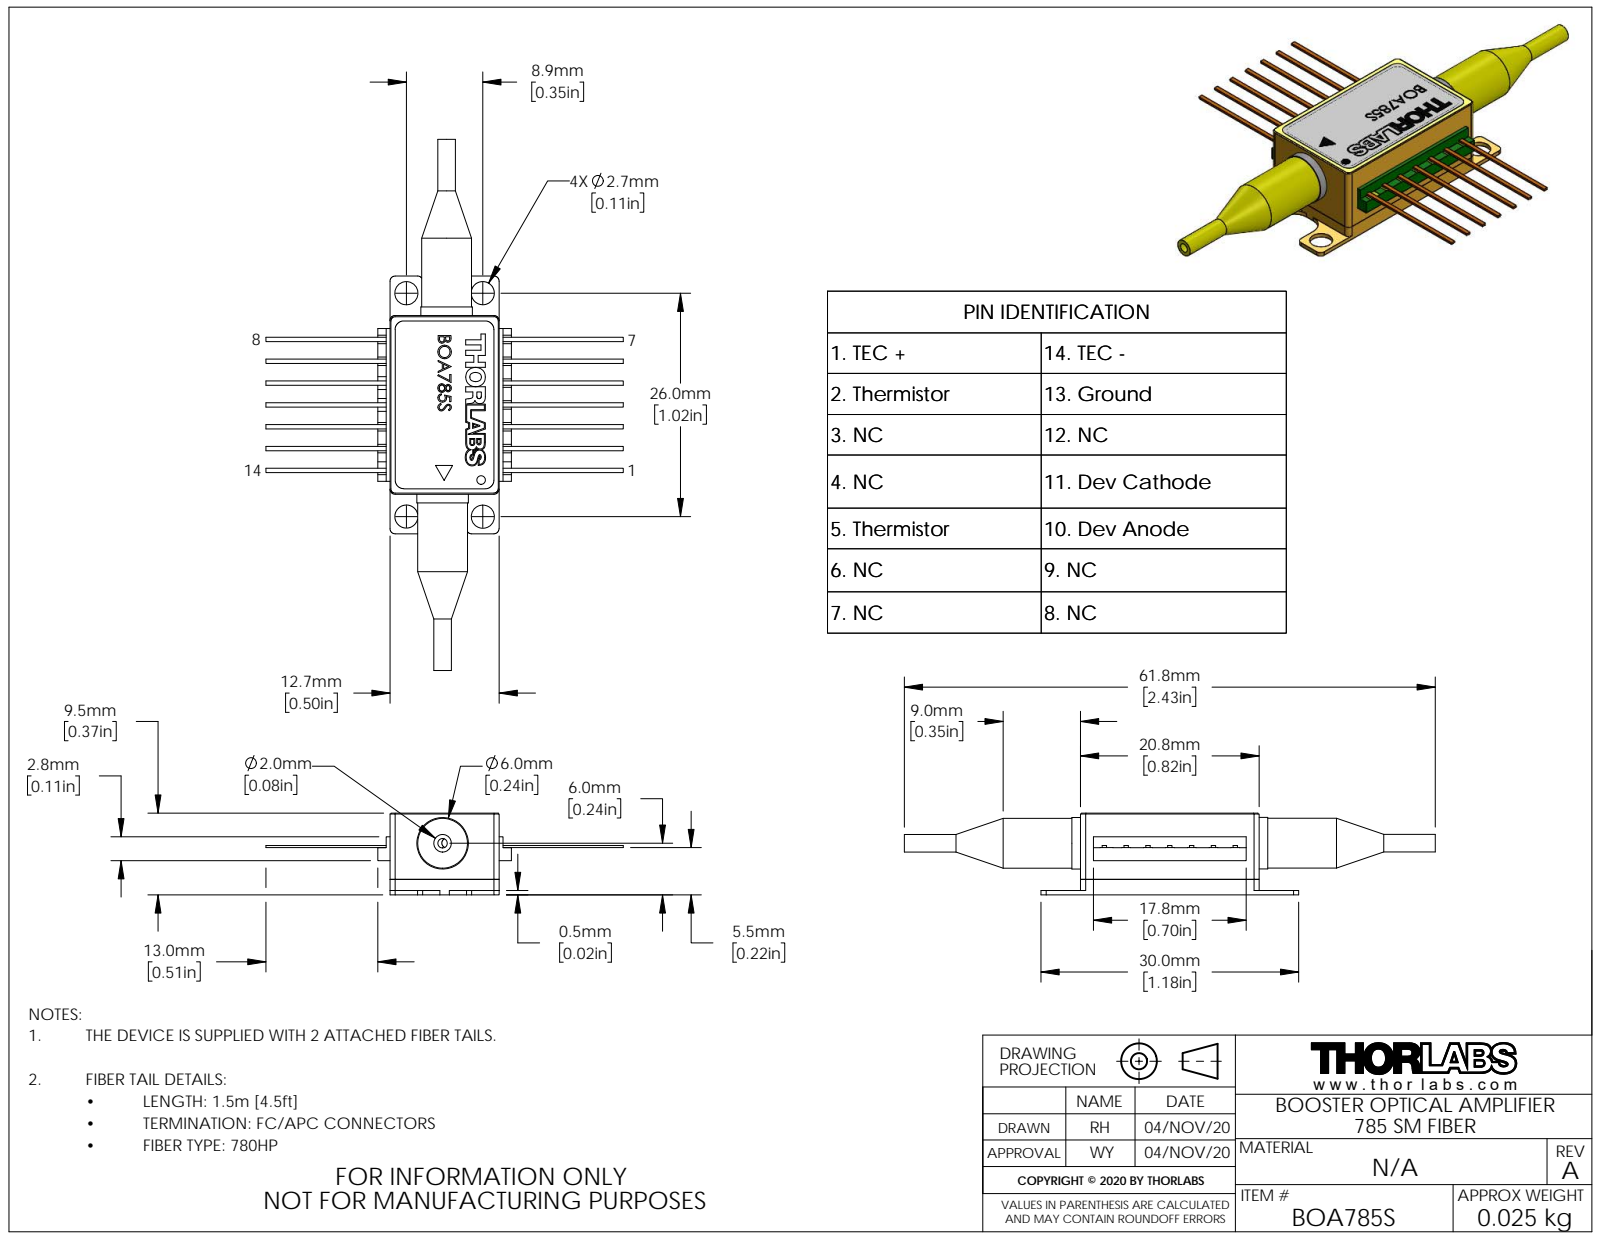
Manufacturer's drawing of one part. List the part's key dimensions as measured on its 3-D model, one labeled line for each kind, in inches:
Part name (STEP PRODUCT): QTN042296-E0W
STEP written by: SolidWorks 2018 (AUTOMOTIVE_DESIGN)
Units: inches
Bodies: 0 solids, 349 faces (251 planar, 52 cylindrical, 46 other)
Overall size (bounding box): 2.433 × 1.638 × 0.374
Round holes (diameter × count): ⌀0.106 ×4, ⌀0.043 ×2, ⌀0.039 ×1
Round bosses / shafts (diameter × count): ⌀0.236 ×2, ⌀0.228 ×2, ⌀0.08 ×2
Partial cylindrical surfaces — rounded edges, fillets, slot ends (radius × count): R0.024 ×12, R0.02 ×4, R0.079 ×4, R0.039 ×2
Main face-to-face distances: 0.373, 0.5, 0.071, 0.302, 0.146, 0.085, 0.156, 0.217, 0.156, 0.06
Hole centre spacings: 0.35, 1.024, 1.082, 0.019, 0.168, 0.382, 0.856, 0.922
